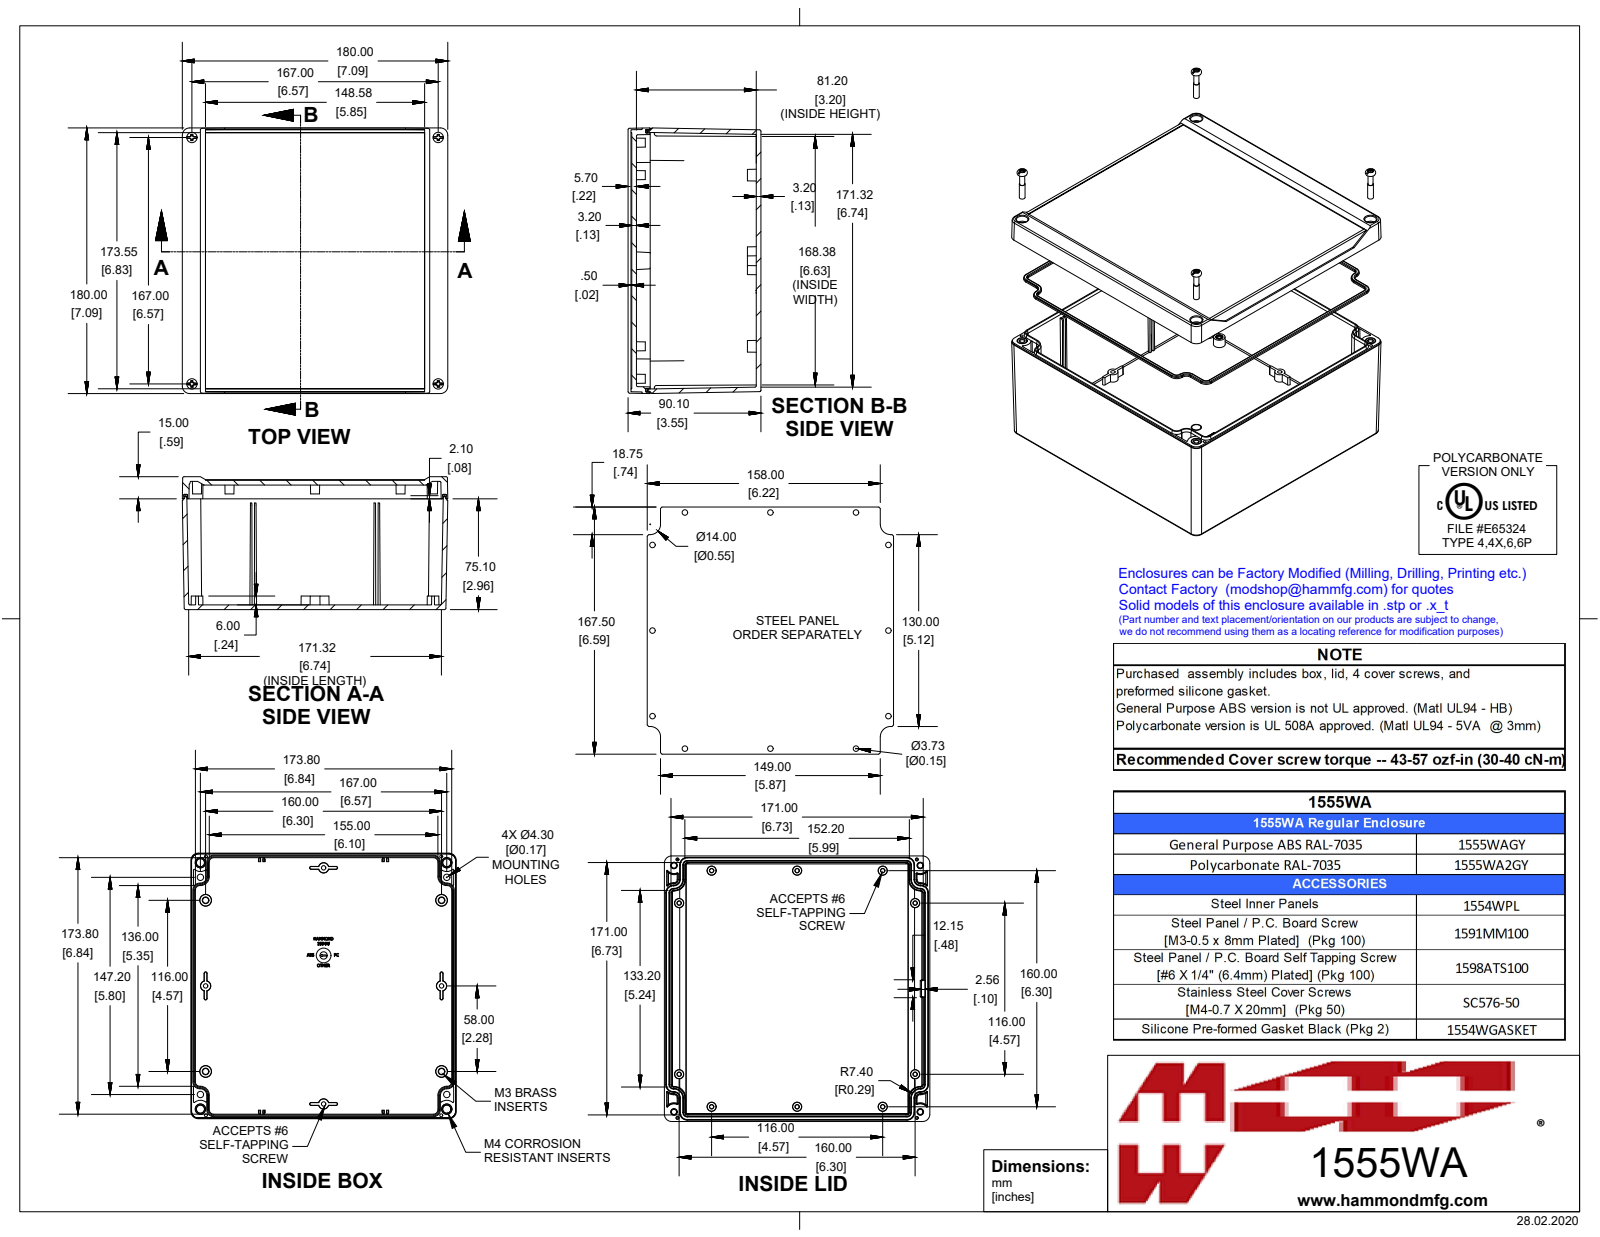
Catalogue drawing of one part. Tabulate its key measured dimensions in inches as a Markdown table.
| quantity | value |
| --- | --- |
| part name | 1555WA2GY |
| STEP written by | SolidWorks 2019 (AUTOMOTIVE_DESIGN) |
| units | inches |
| bodies | 15 solids, 1940 faces (661 planar, 385 cylindrical, 894 other) |
| overall size | 7.087 × 7.087 × 3.547 |
| volume | 25.64 in³ |
| surface area | 439.7 in² |
| round holes (diameter × count) | 0.097 × 4, 0.128 × 4, 0.181 × 4, 0.138 × 3 |
| round bosses / shafts (diameter × count) | 0.25 × 4, 0.218 × 4, 0.21 × 4, 0.19 × 4, 0.154 × 4, 0.153 × 4, 0.15 × 4, 0.135 × 4 |
| partial cylindrical surfaces (radius × count) | 0.02 × 26, 0.012 × 22, 0.039 × 12, 0.031 × 10, 0.104 × 8, 0.118 × 8, 0.197 × 8, 0.199 × 8 |
| main face-to-face distances | 0.126, 3.323, 0.122, 3.449, 3.197, 7.087, 6.965, 6.909, 0.098, 0.177 |
| hole center spacings | 1.013, 5.572, 6.515, 6.575, 8.513, 4.567, 6.299, 7.781 |
